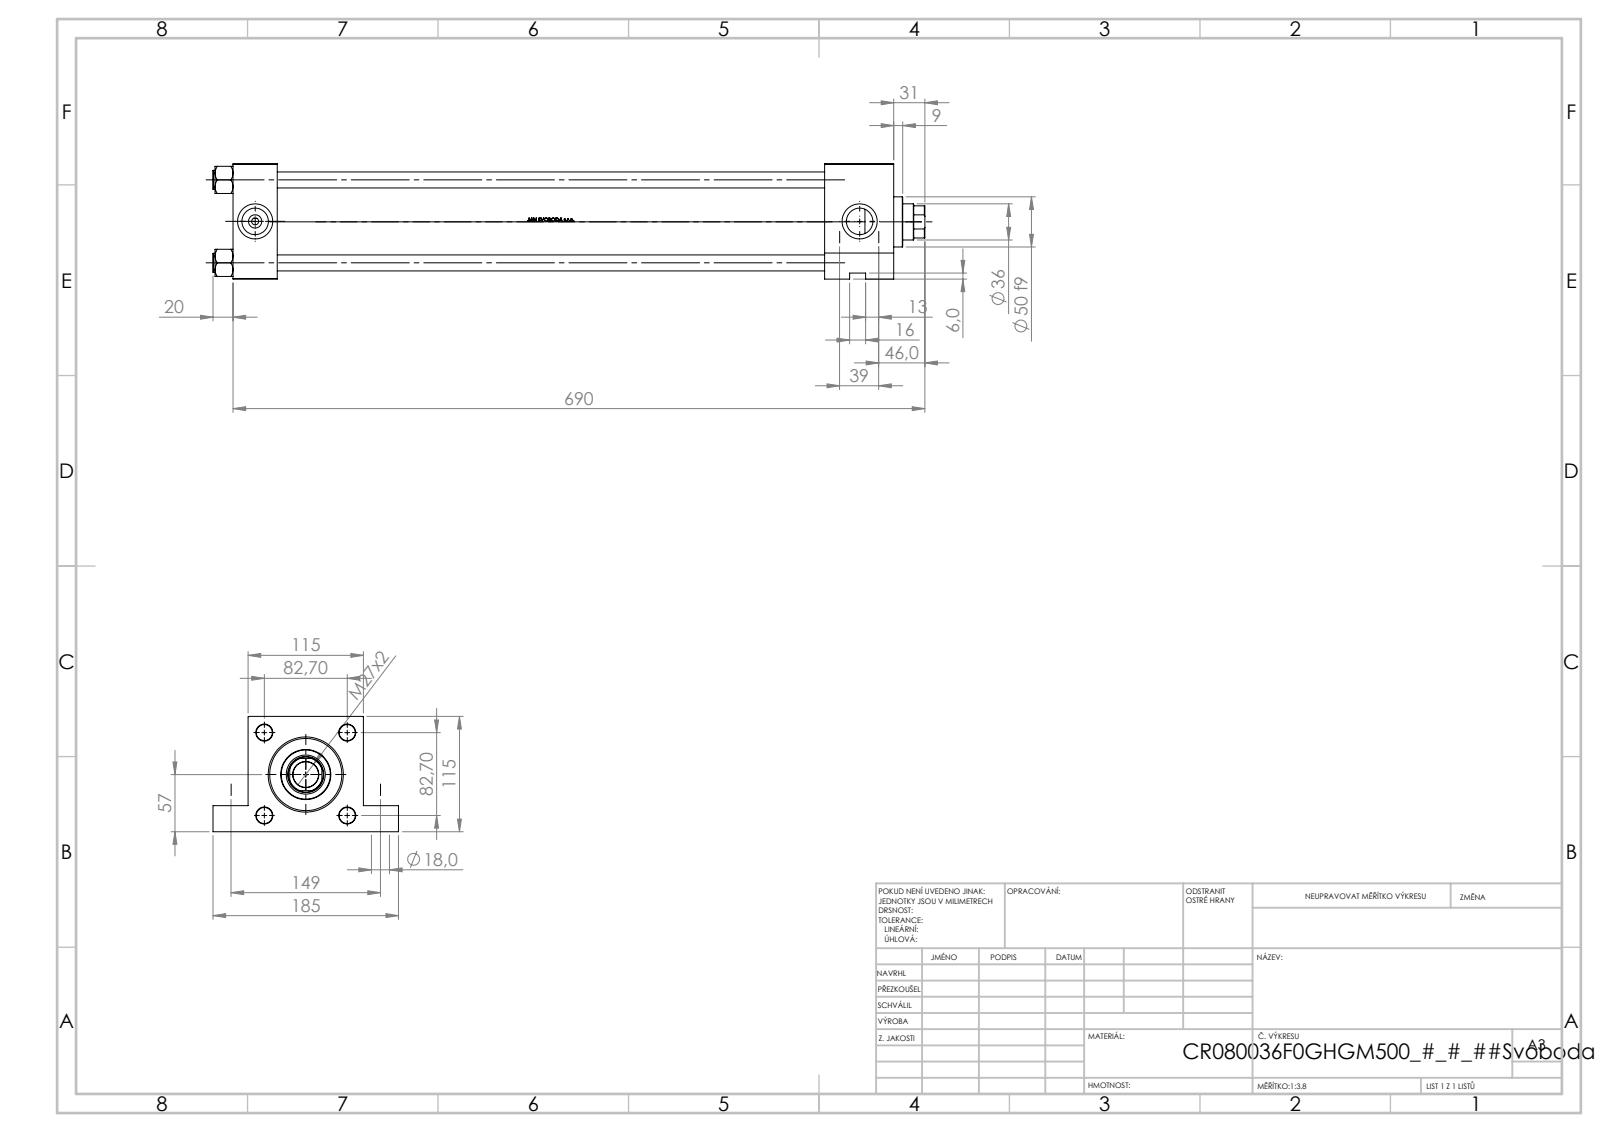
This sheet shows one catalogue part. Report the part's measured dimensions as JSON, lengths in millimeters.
{"part_name": "V215CR_F_Body; NUT_M5_F; V215_VC_A; V215CR_VCP_F (+1 more)", "step_written_by": "SolidWorks 2019 (CONFIG_CONTROL_DESIGN)", "units": "millimeters", "bodies": {"solids": 11, "faces": 1151, "planar": 485, "cylindrical": 126, "other": 540}, "overall_size": [710, 185, 115], "volume_mm3": 3133000, "surface_area_mm2": 684696, "round_holes": [[16, 4], [18, 4], [7, 2], [26.44, 2], [35, 2], [25.5, 1], [36, 1], [39, 1], [61, 1], [72, 1], [80, 1]], "round_bosses_or_shafts": [[19, 4], [86, 1], [50, 1]], "partial_cylinders_radius": [[17.5, 1]], "face_to_face_distances": [115, 44, 615, 659, 590, 546, 69, 630.3, 586.3, 40.3], "hole_center_spacings": [82.7, 39, 58.13, 58.83, 116.96, 149, 154.02, 603]}
